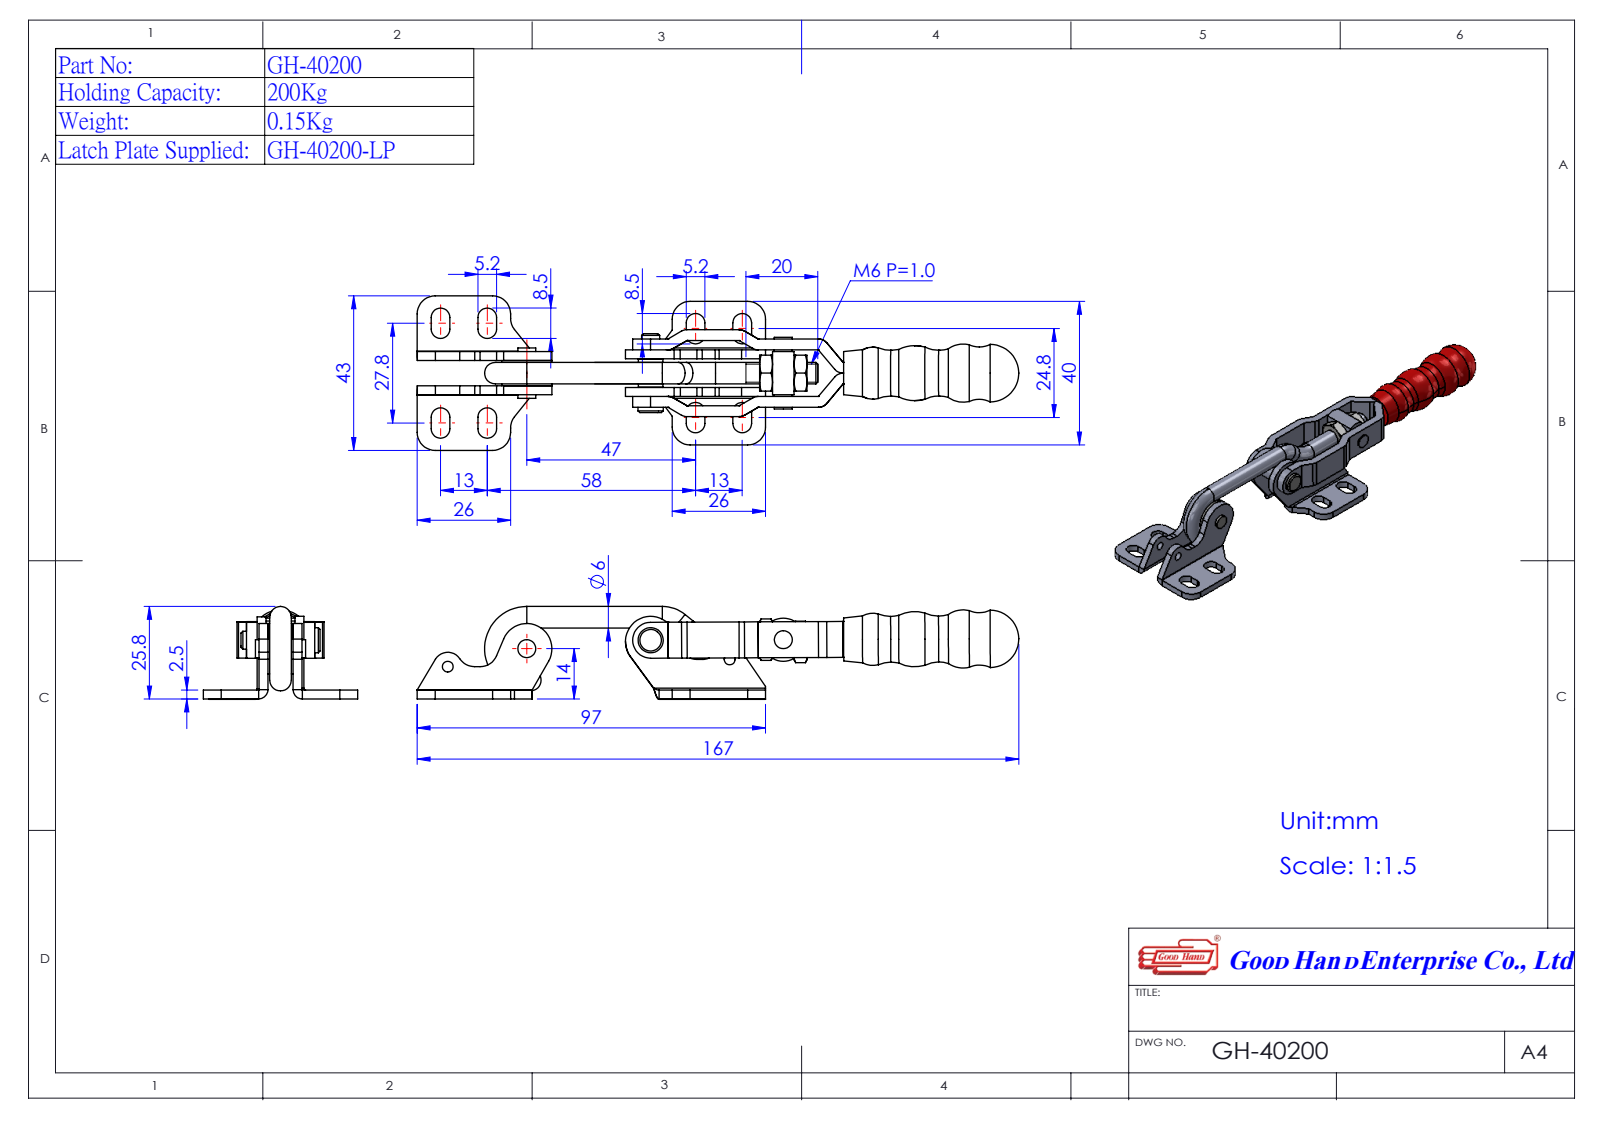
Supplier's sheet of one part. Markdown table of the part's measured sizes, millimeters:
| quantity | value |
| --- | --- |
| part name | GH-40200(簡化); Group2^GH-40200(簡化); Group1^GH-40200(簡化); 440200-h-1^GH-40200(簡化) (+2 more) |
| STEP written by | SolidWorks 2016 (AUTOMOTIVE_DESIGN) |
| units | millimeters |
| bodies | 6 solids, 421 faces (184 planar, 153 cylindrical, 84 other) |
| overall size | 167 × 43 × 25.25 |
| volume | 25 108 mm³ |
| surface area | 17 950 mm² |
| round holes (diameter × count) | 4 × 3, 3 × 2, 5 × 1, 6 × 1, 8 × 1 |
| round bosses / shafts (diameter × count) | 6 × 3, 14 × 2, 5 × 2, 7 × 1 |
| partial cylindrical surfaces (radius × count) | 2.6 × 18, 3.01 × 12, 5 × 11, 2.5 × 4, 0.1 × 2, 0.5 × 2, 3 × 2, 4 × 2 |
| main face-to-face distances | 2.5, 3, 10, 0.5, 13, 12.5, 10.5, 16, 2.6, 5.6 |
| hole center spacings | 22.56, 15.75, 34.05, 36.94, 56.07, 56.43, 70.96, 78.02 |
